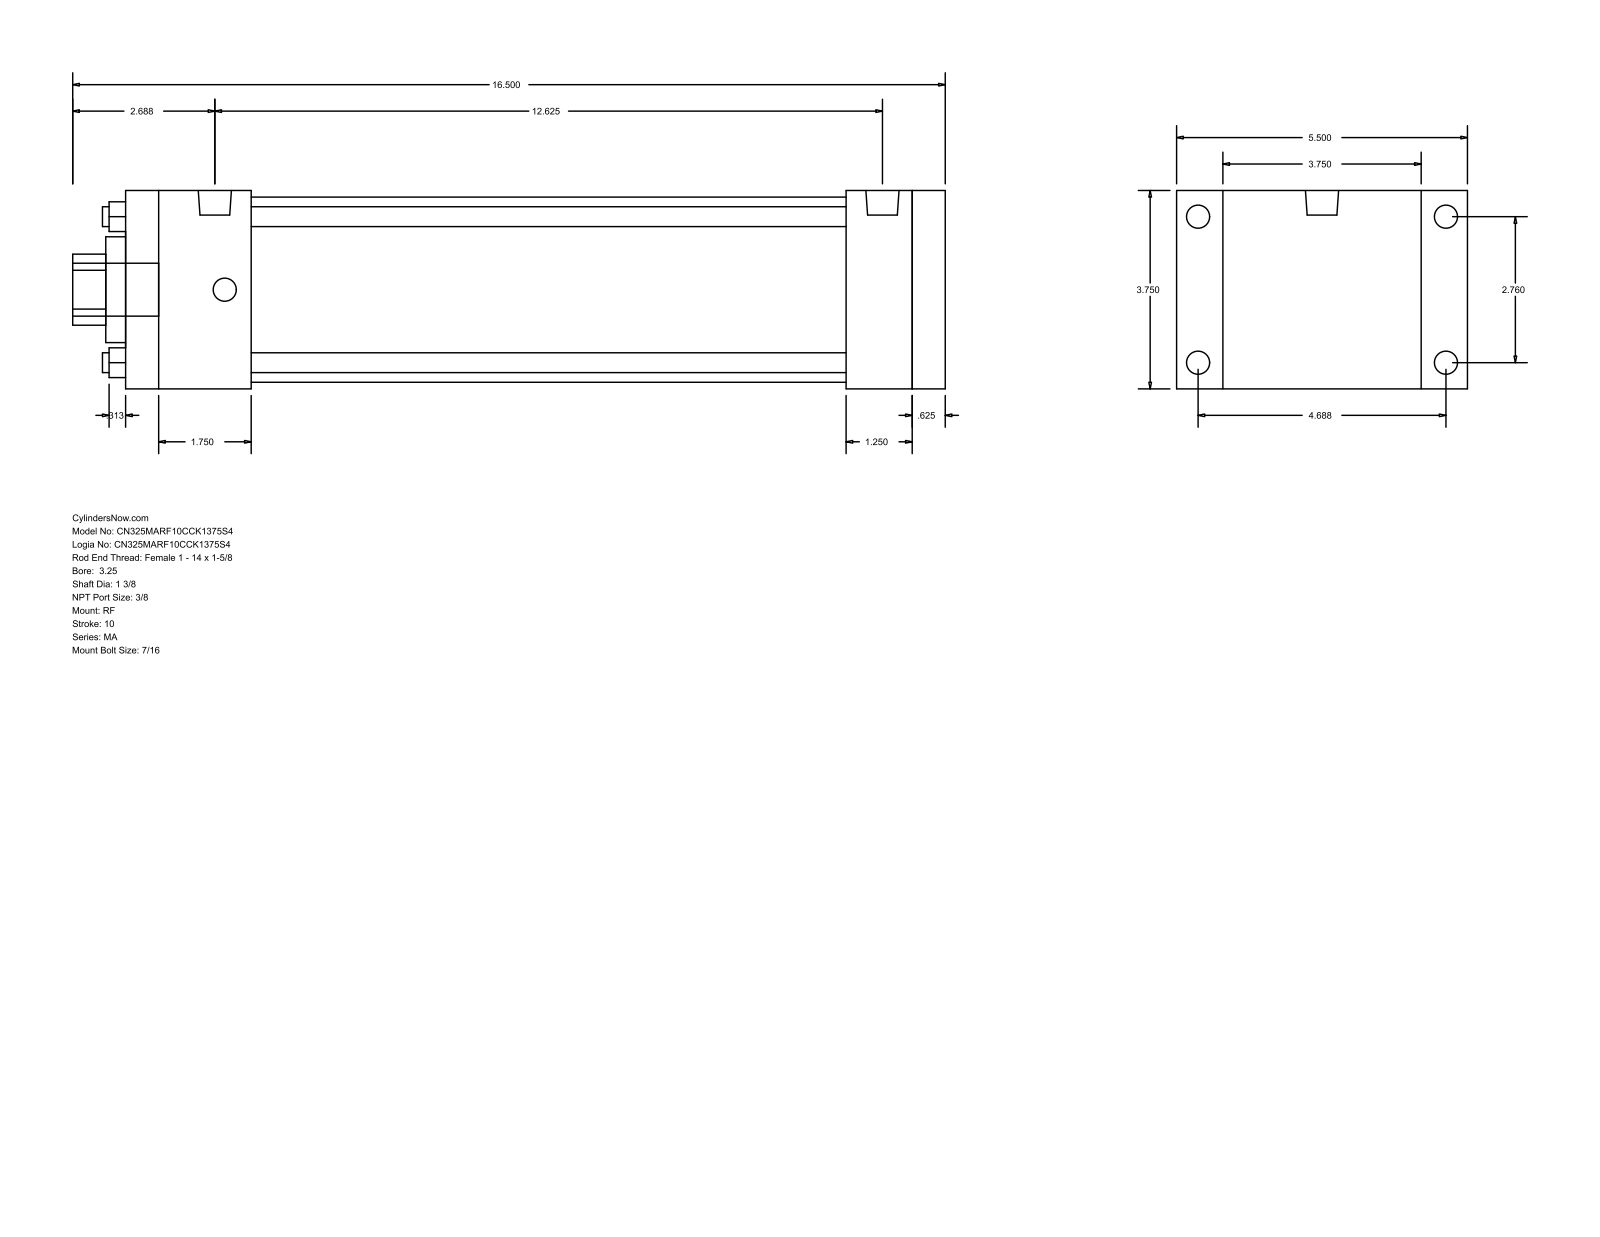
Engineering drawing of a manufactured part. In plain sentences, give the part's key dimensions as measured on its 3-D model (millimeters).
The part is named "MA_RF__0325_1.375". Its 3-D file was written by "GSSL Pune (CONFIG_CONTROL_DESIGN)". It is 0 solids with 92 faces: 64 planar, 28 cylindrical and 0 other. Overall it measures 419.1 by 139.7 by 95.25 millimeters. Round holes: 4 of diameter 9.53, 1 of diameter 34.92, 1 of diameter 50.8, 1 of diameter 88.9. Round bosses or shafts: 8 of diameter 11.11, 2 of diameter 15.93, 1 of diameter 25.4. Partial cylindrical surfaces (rounded edges, fillets, slot ends): 1 of radius 17.06. The main face-to-face distances are 95.24, 393.7, 15.87, 377.83, 22.23, 117.47, 346.08, 31.75, 47.62, 60.32. The hole center spacings are 49.57, 70.1, 99.14.
